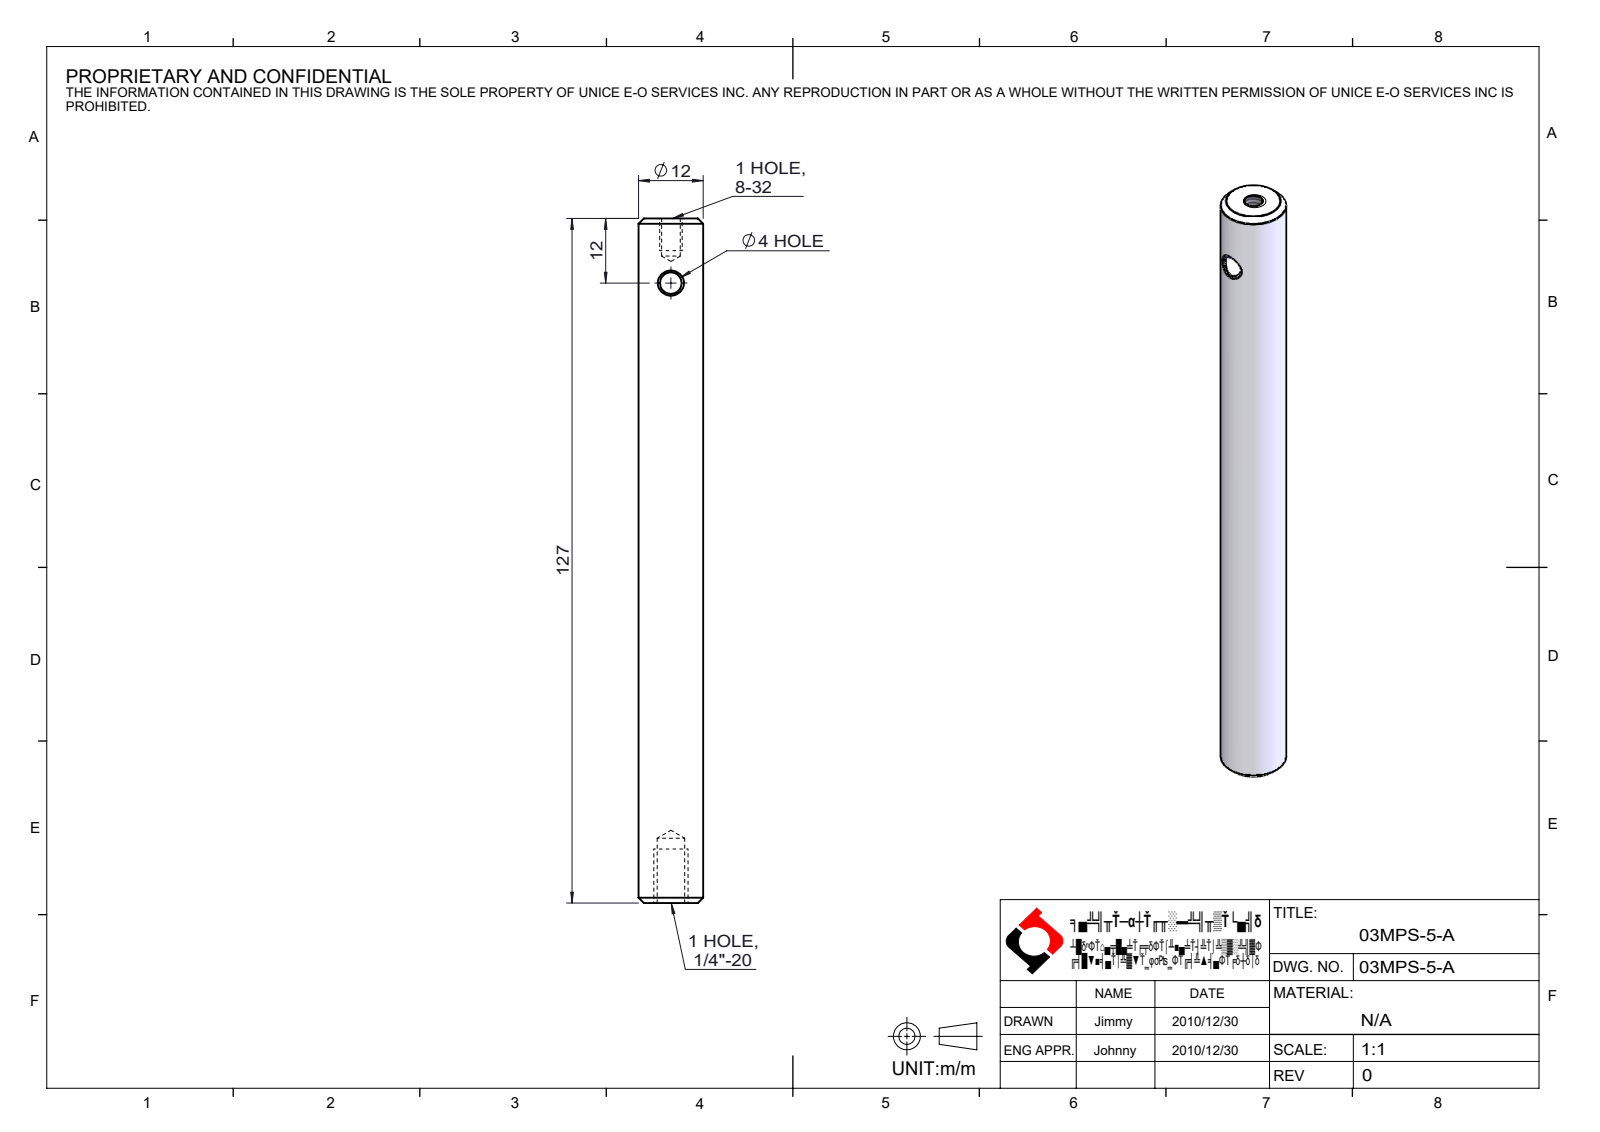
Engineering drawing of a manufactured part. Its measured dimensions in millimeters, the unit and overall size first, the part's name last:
Units: millimetres
Overall size (bounding box): 127 × 12 × 12
Round holes (diameter × count): ⌀3.45 ×1, ⌀4 ×1, ⌀5.11 ×1
Round bosses / shafts (diameter × count): ⌀12 ×1
Main face-to-face distances: 127
Volume: 13 853 mm³ · Surface area: 5 355 mm²
Bodies: 1 solid, 22 faces (2 planar, 8 cylindrical, 12 other)
Part name (STEP PRODUCT): 03MPS-5-A
STEP written by: SolidWorks 2021 (CONFIG_CONTROL_DESIGN)
